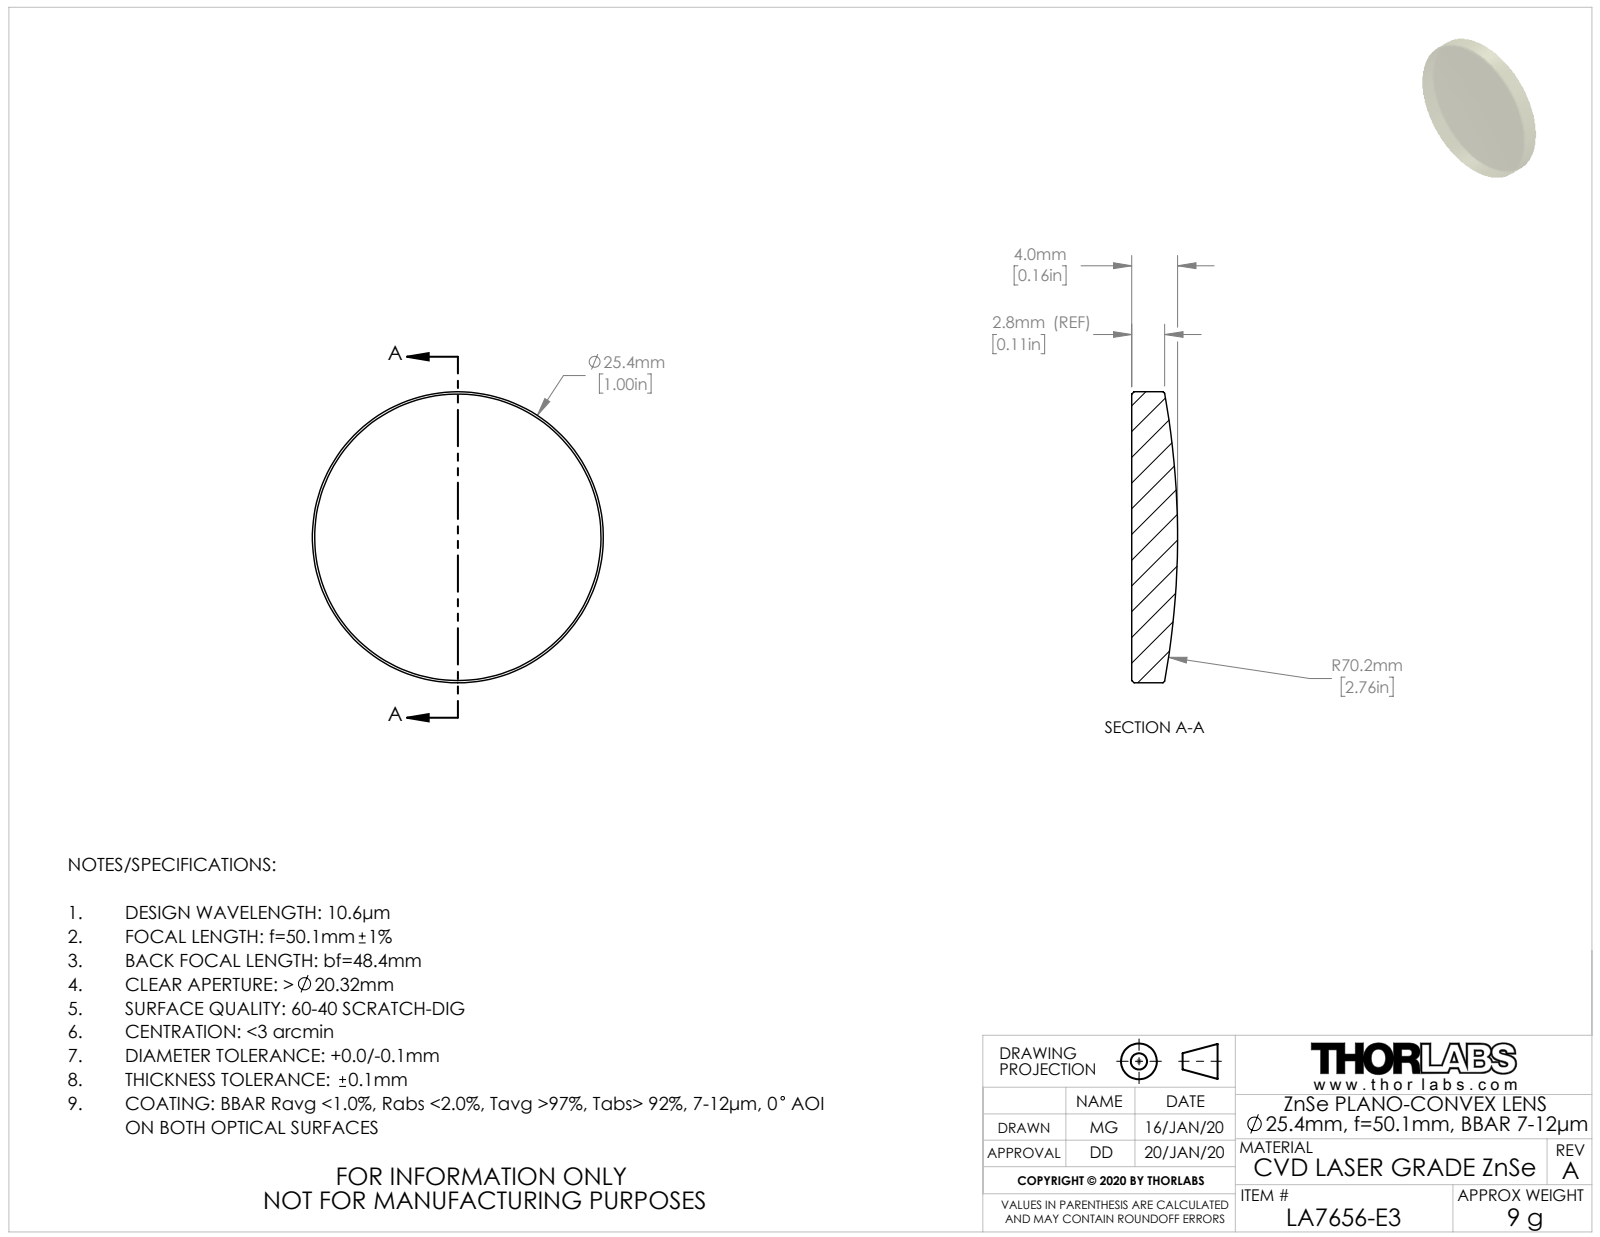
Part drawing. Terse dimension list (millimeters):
name: TTN206066-E0W
written by: SolidWorks 2018 (CONFIG_CONTROL_DESIGN)
unit: mm
bodies: 1 solid, 9 faces (1 planar, 2 cylindrical, 6 other)
size: 25.4 × 25.4 × 4
volume: 1 732 mm³; area: 1 230 mm²
bosses: 1× ⌀25.4
